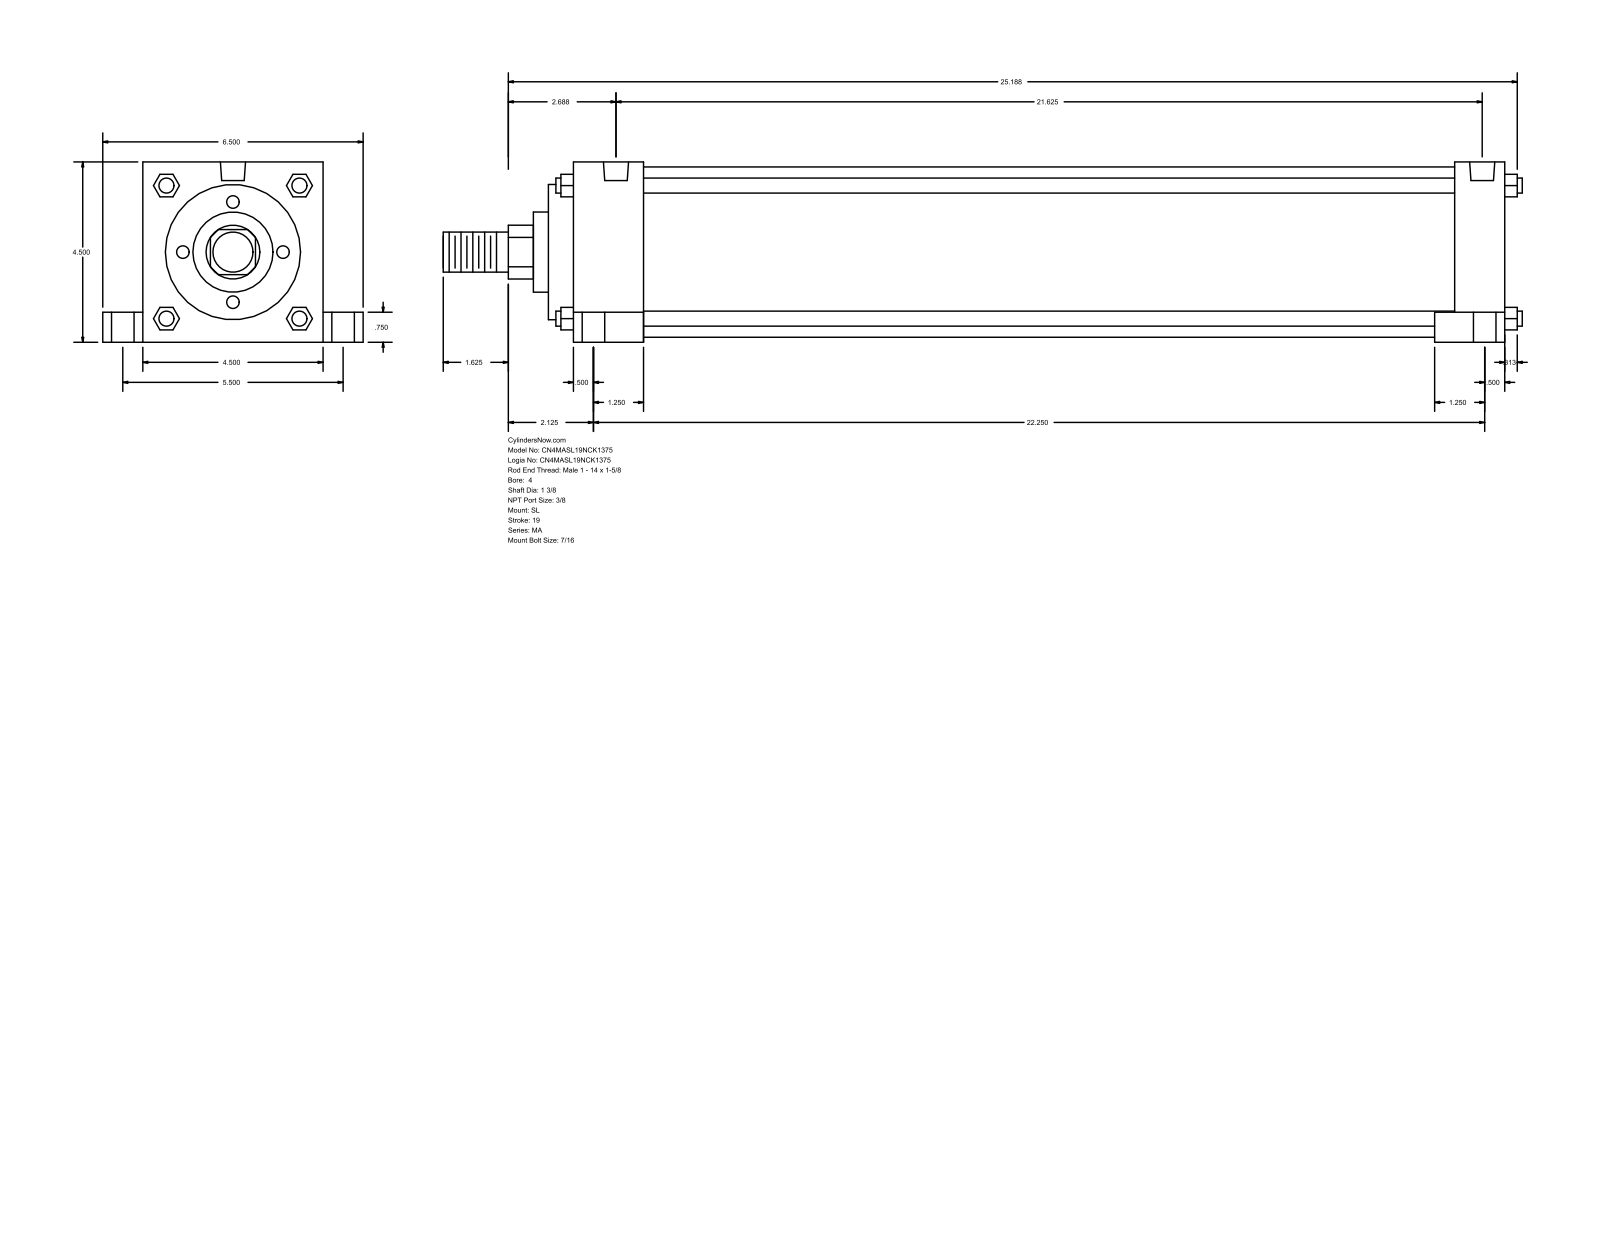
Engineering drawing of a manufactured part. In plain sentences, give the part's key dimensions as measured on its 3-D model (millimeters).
The part is named "MA_SL__0400_1.375". Its 3-D file was written by "GSSL Pune (CONFIG_CONTROL_DESIGN)". It is 0 solids with 150 faces: 113 planar, 37 cylindrical and 0 other. Overall it measures 684.21 by 165.1 by 114.3 millimeters. Round holes: 4 of diameter 11.11, 4 of diameter 14.29, 4 of diameter 20.64, 2 of diameter 15.93. Round bosses or shafts: 4 of diameter 9.53, 1 of diameter 107.95, 1 of diameter 85.72, 1 of diameter 50.8, 1 of diameter 34.92, 1 of diameter 25.4. Partial cylindrical surfaces (rounded edges, fillets, slot ends): 1 of radius 17.06. The main face-to-face distances are 114.3, 590.56, 15.87, 606.43, 60.32, 44.45, 546.11, 574.68, 558.81, 514.36. The hole center spacings are 4.77, 69.87, 70.14, 71.29, 72.4, 139.7, 539.74, 544.51.
